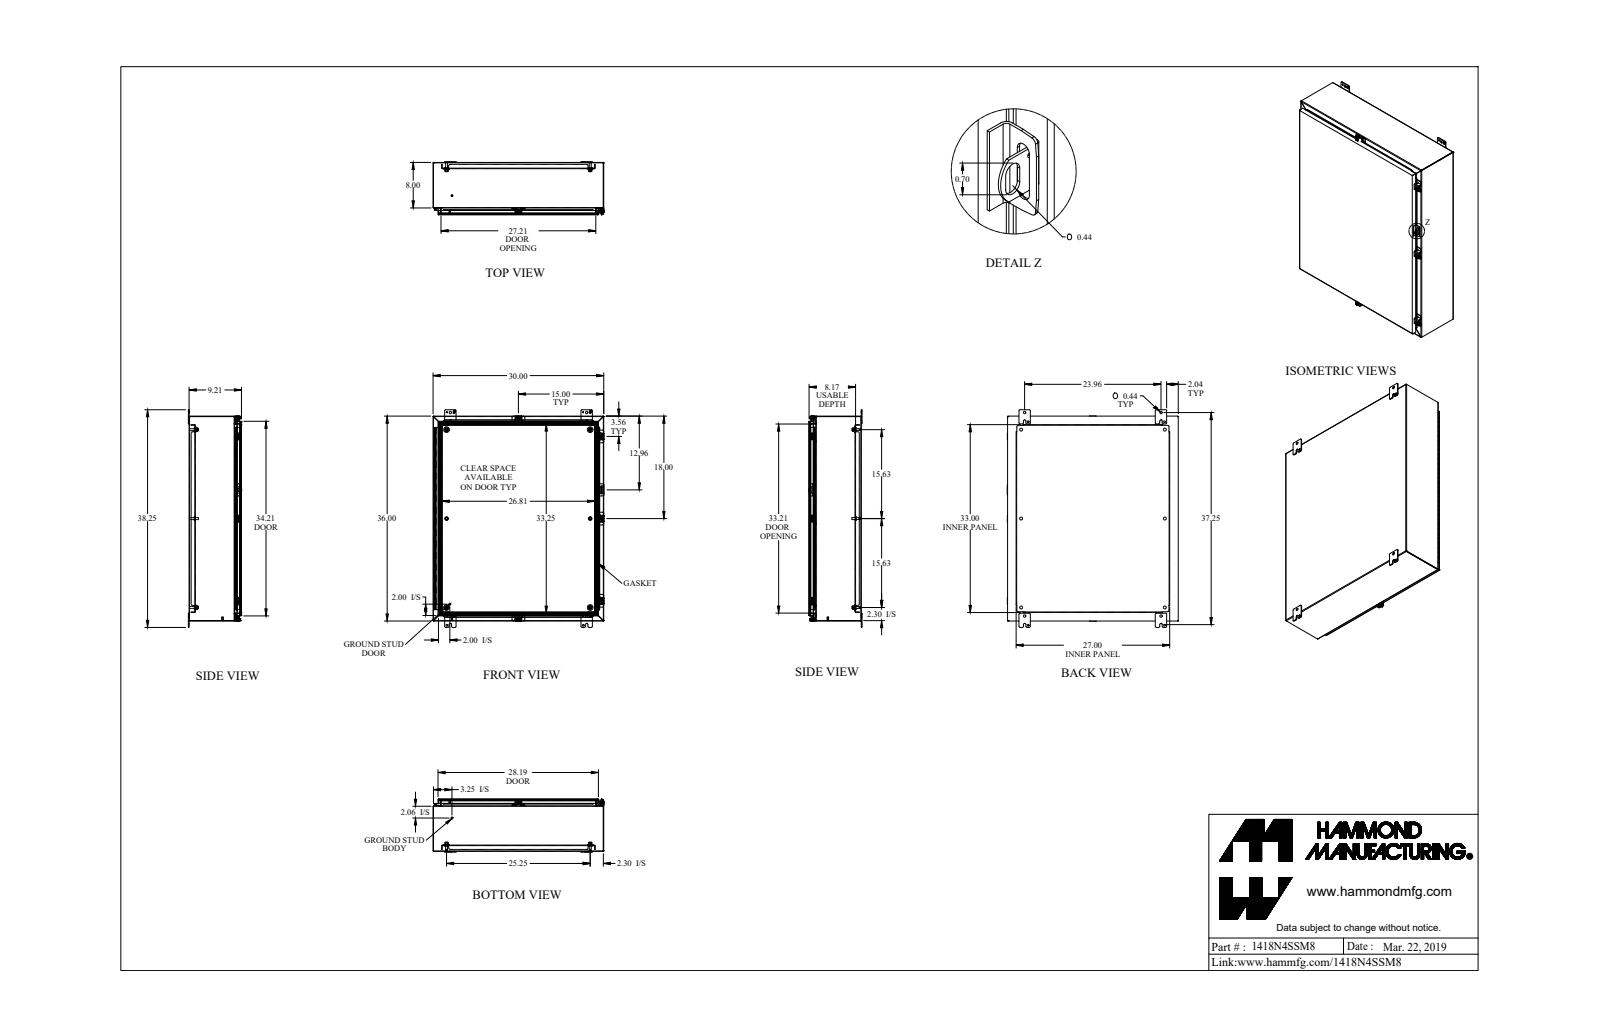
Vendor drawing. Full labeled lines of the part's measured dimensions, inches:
Part name (STEP PRODUCT): 1418N4SSM8_Default
STEP written by: SolidWorks 2019 (CONFIG_CONTROL_DESIGN)
Units: inches
Bodies: 49 solids, 1845 faces (1109 planar, 630 cylindrical, 106 other)
Overall size (bounding box): 38.25 × 30.063 × 9.375
Volume: 365.7 in³ · Surface area: 9 528 in²
Round holes (diameter × count): ⌀0.5 ×6, ⌀0.213 ×5, ⌀0.265 ×5, ⌀0.375 ×5, ⌀0.307 ×4, ⌀0.313 ×4, ⌀0.437 ×4, ⌀0.445 ×4, ⌀0.125 ×1, ⌀0.187 ×1
Round bosses / shafts (diameter × count): ⌀0.65 ×6, ⌀0.375 ×6, ⌀0.332 ×6, ⌀0.5 ×5, ⌀0.39 ×5, ⌀0.244 ×5, ⌀1 ×4, ⌀0.313 ×2
Partial cylindrical surfaces — rounded edges, fillets, slot ends (radius × count): R0.25 ×32, R0.048 ×27, R0.143 ×27, R0.188 ×26, R0.036 ×24, R0.108 ×24, R0.125 ×12, R0.141 ×10
Main face-to-face distances: 0.072, 0.072, 9.066, 9.138, 9.138, 0.095, 9.21, 0.937, 1.009, 8.106
Hole centre spacings: 15.625, 25.25, 12.802, 21.782, 31.25, 35.683, 43.039, 12.803
